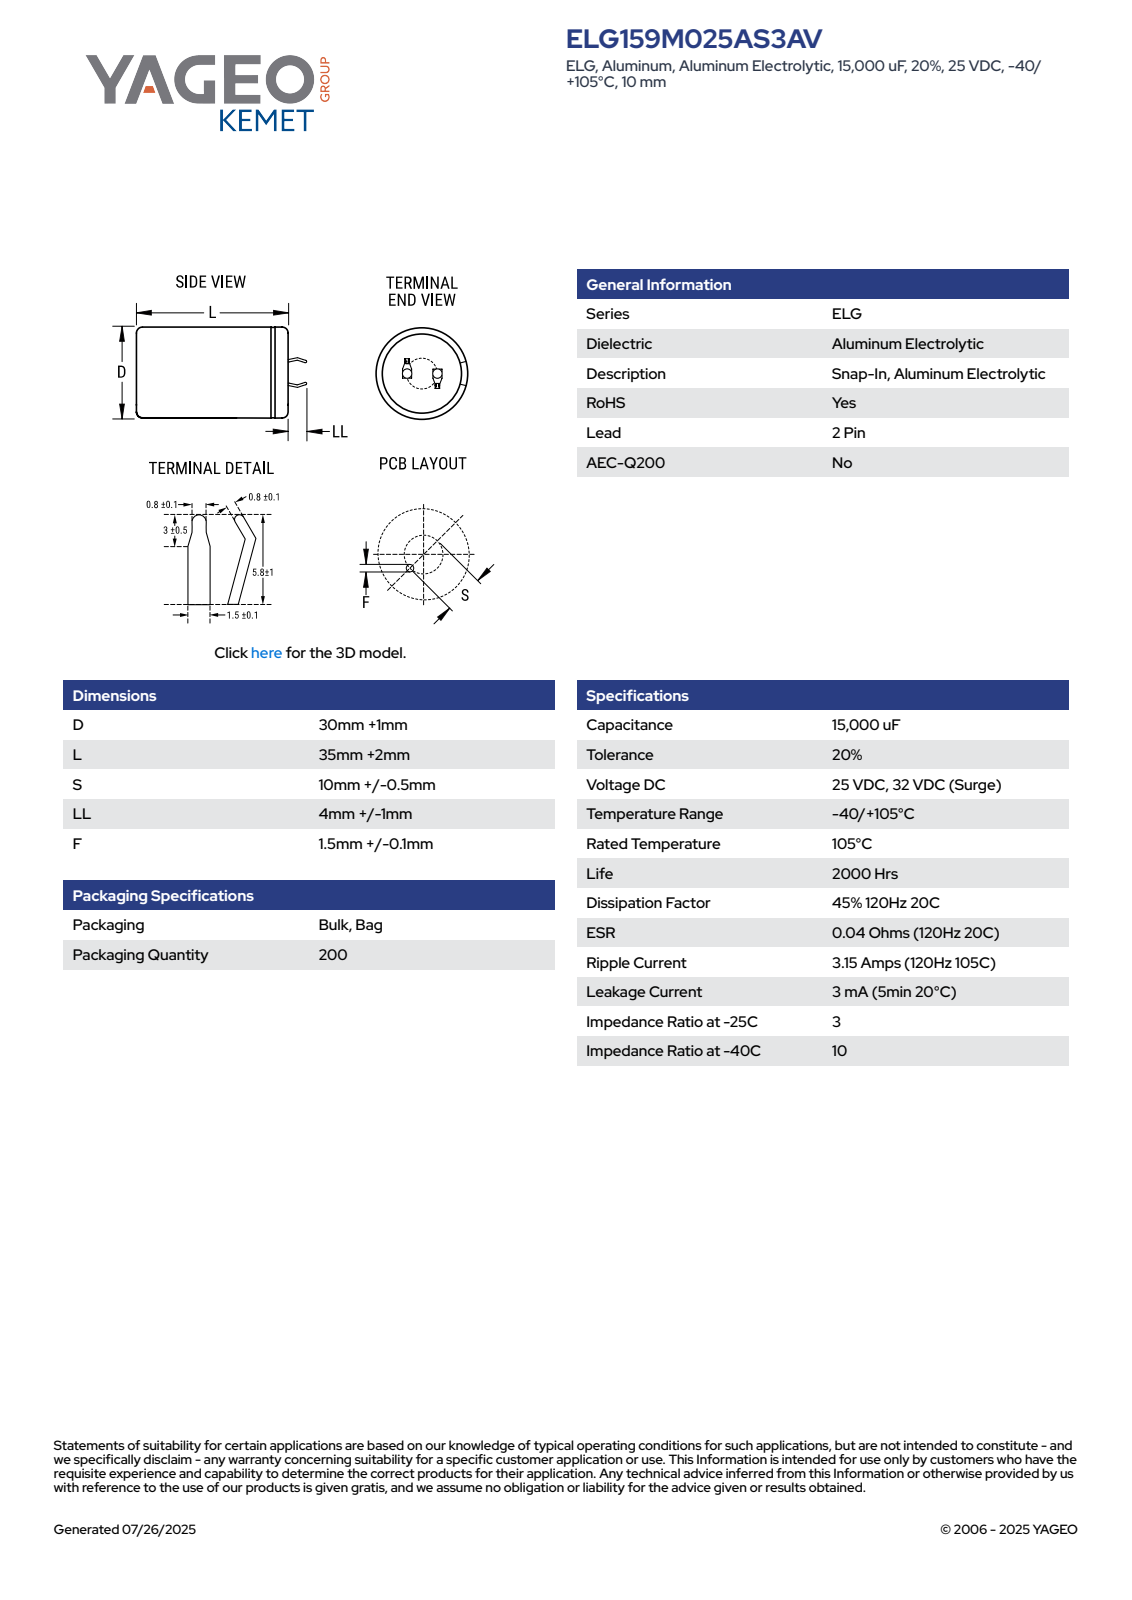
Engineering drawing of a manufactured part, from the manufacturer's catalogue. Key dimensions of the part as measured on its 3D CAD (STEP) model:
Part name (STEP PRODUCT): CARS_K2P_30X35_D31L37S10LL5F1.6
STEP written by: SolidWorks 2014 (AUTOMOTIVE_DESIGN)
Units: millimetres
Bodies: 1 solid, 100 faces (52 planar, 9 cylindrical, 39 other)
Overall size (bounding box): 41.99 × 31 × 31
Volume: 27 591 mm³ · Surface area: 5 112 mm²
Round holes (diameter × count): ⌀27.43 ×1
Round bosses / shafts (diameter × count): ⌀31 ×1
Partial cylindrical surfaces — rounded edges, fillets, slot ends (radius × count): R15.49 ×1
Main face-to-face distances: 36.99, 37.49, 0.5, 7.08, 0.6, 0.59, 7.6, 0.75, 1.35, 7.68
